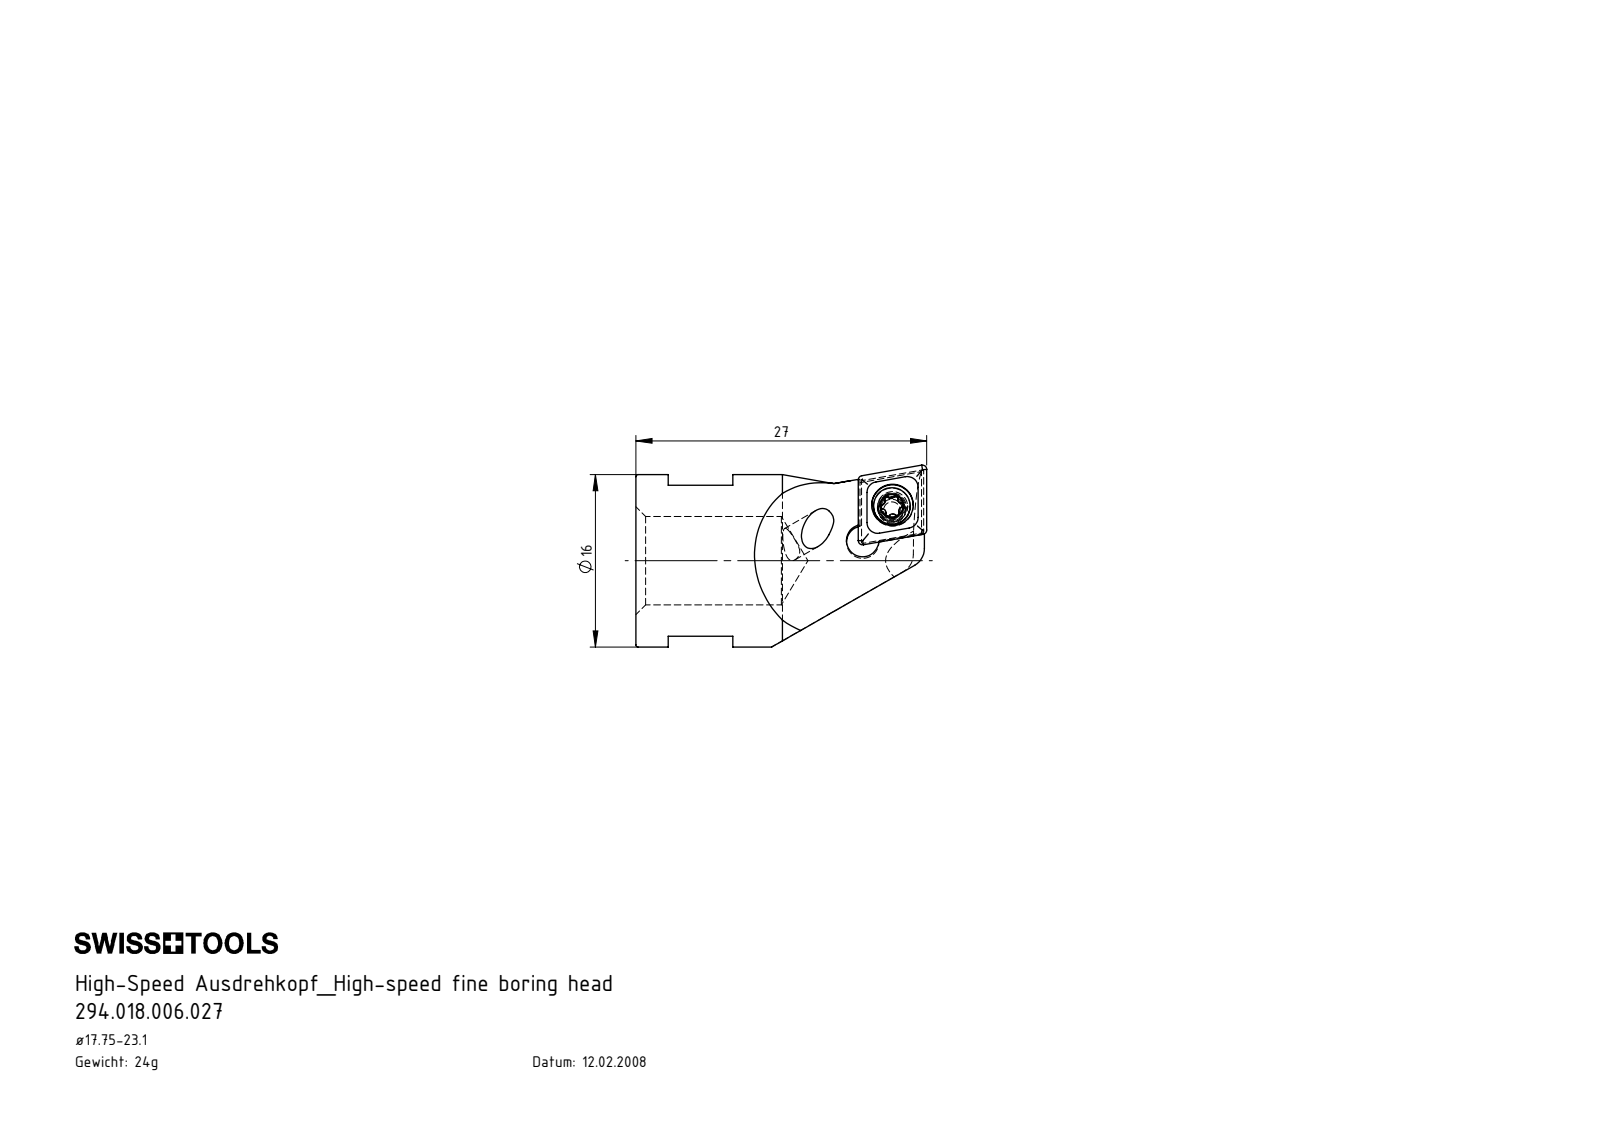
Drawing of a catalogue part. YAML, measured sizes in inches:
part_name: "CCMT060204; WCA-ER2.001.006_A; HS0-A18.K11.027_B; HS0.A18.K11.027"
step_written_by: "SolidWorks 2017 (AUTOMOTIVE_DESIGN)"
units: inches
bodies: {solids: 3, faces: 123, planar: 34, cylindrical: 35, other: 54}
overall_size: [1.063, 0.665, 0.63]
volume: 0.184
surface_area: 3.19
round_holes:
  - {diameter: 0.081, count: 1}
  - {diameter: 0.11, count: 1}
  - {diameter: 0.118, count: 1}
  - {diameter: 0.152, count: 1}
  - {diameter: 0.323, count: 1}
round_bosses_or_shafts:
  - {diameter: 0.63, count: 1}
  - {diameter: 0.134, count: 1}
  - {diameter: 0.098, count: 1}
partial_cylinders:
  - {radius: 0.008, count: 6}
  - {radius: 0.014, count: 5}
  - {radius: 0.014, count: 1}
  - {radius: 0.059, count: 1}
  - {radius: 0.071, count: 1}
  - {radius: 0.079, count: 1}
face_to_face_distances: [0.552, 0.09, 0.236, 0.094, 0.354, 0.118, 0.819, 0.701, 0.465, 0.058]
